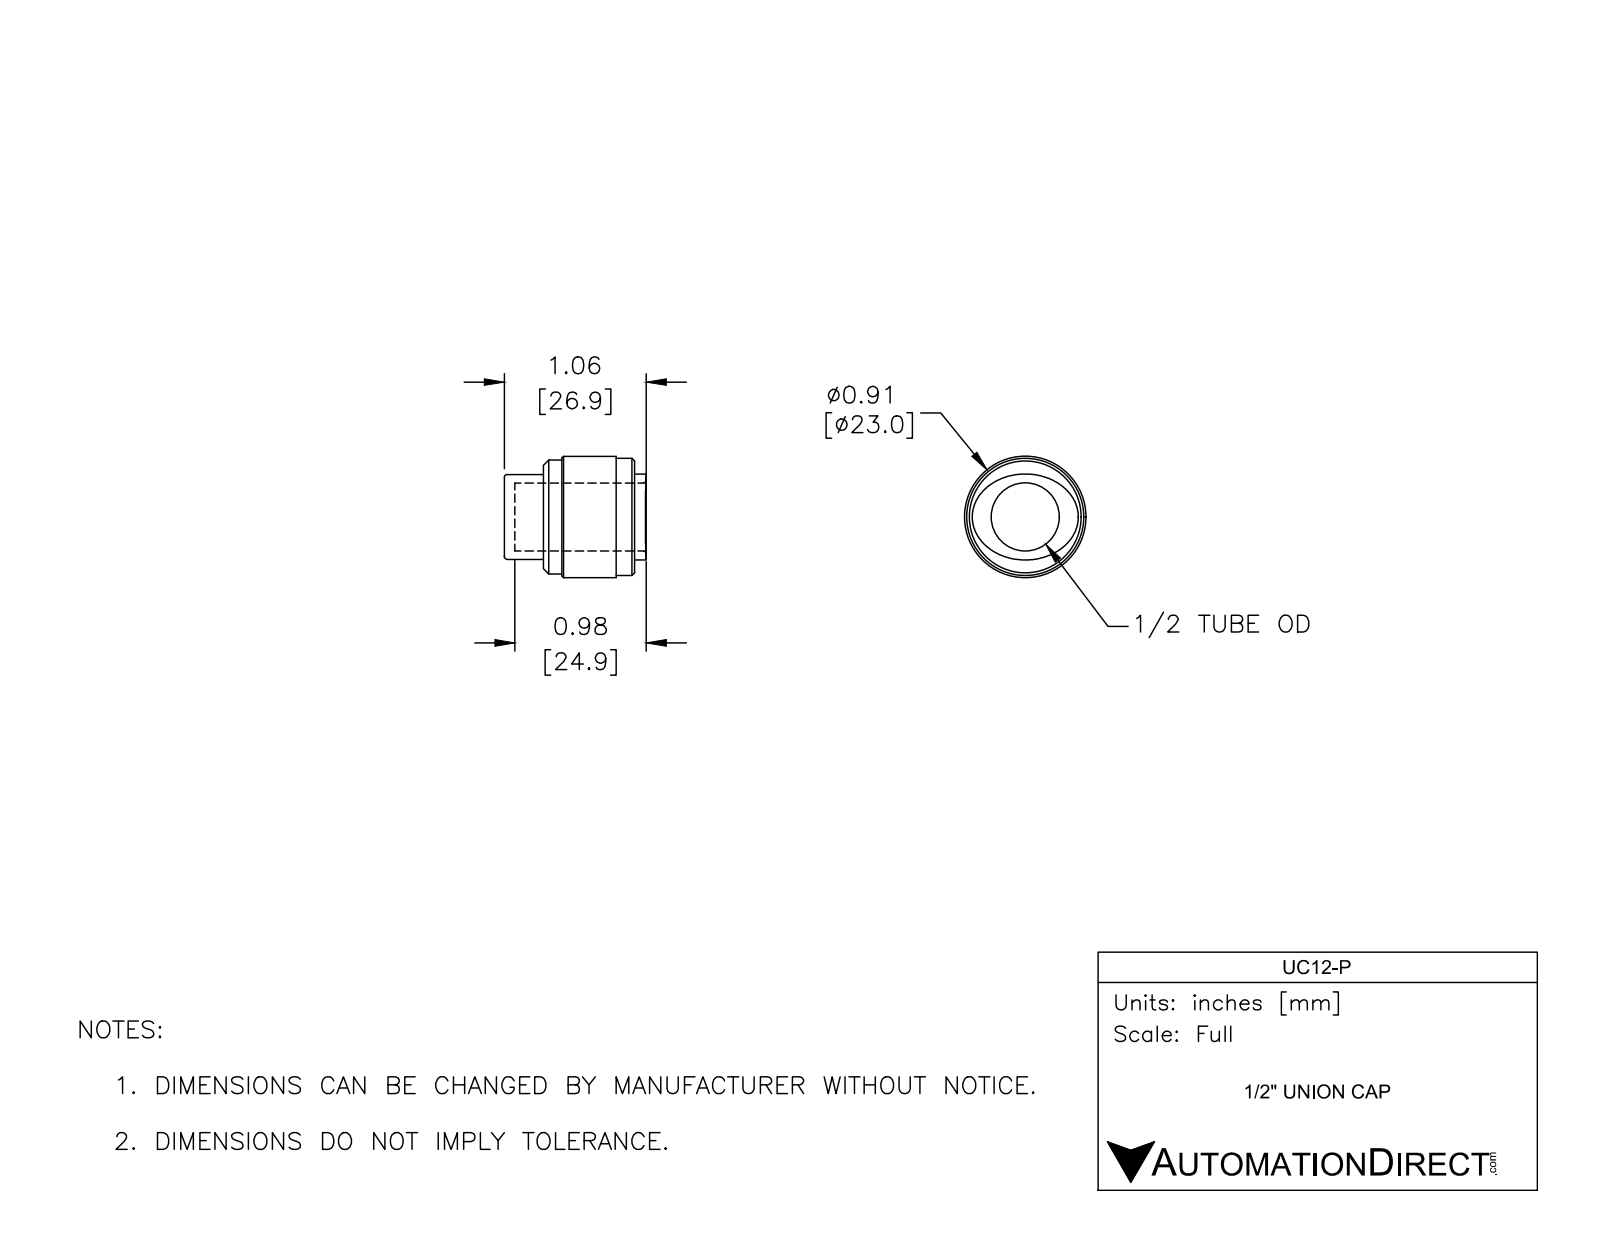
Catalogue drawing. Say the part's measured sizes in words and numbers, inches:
The part is named "UC12-P". Its 3-D file was written by "SolidWorks 2017 (AUTOMOTIVE_DESIGN)". It is 1 solid with 33 faces: 7 planar, 10 cylindrical and 16 other. Overall it measures 1.059 by 0.906 by 0.906 inches. Its volume is 0.347 cubic inches and its surface area 5.374 square inches. Round holes: 1 of diameter 0.508. Round bosses or shafts: 1 of diameter 0.906, 1 of diameter 0.874, 1 of diameter 0.85, 1 of diameter 0.634. The main face-to-face distances are 0.079, 0.291, 0.213, 0.972, 0.894, 0.681, 0.138, 0.543, 0.835, 0.756.
